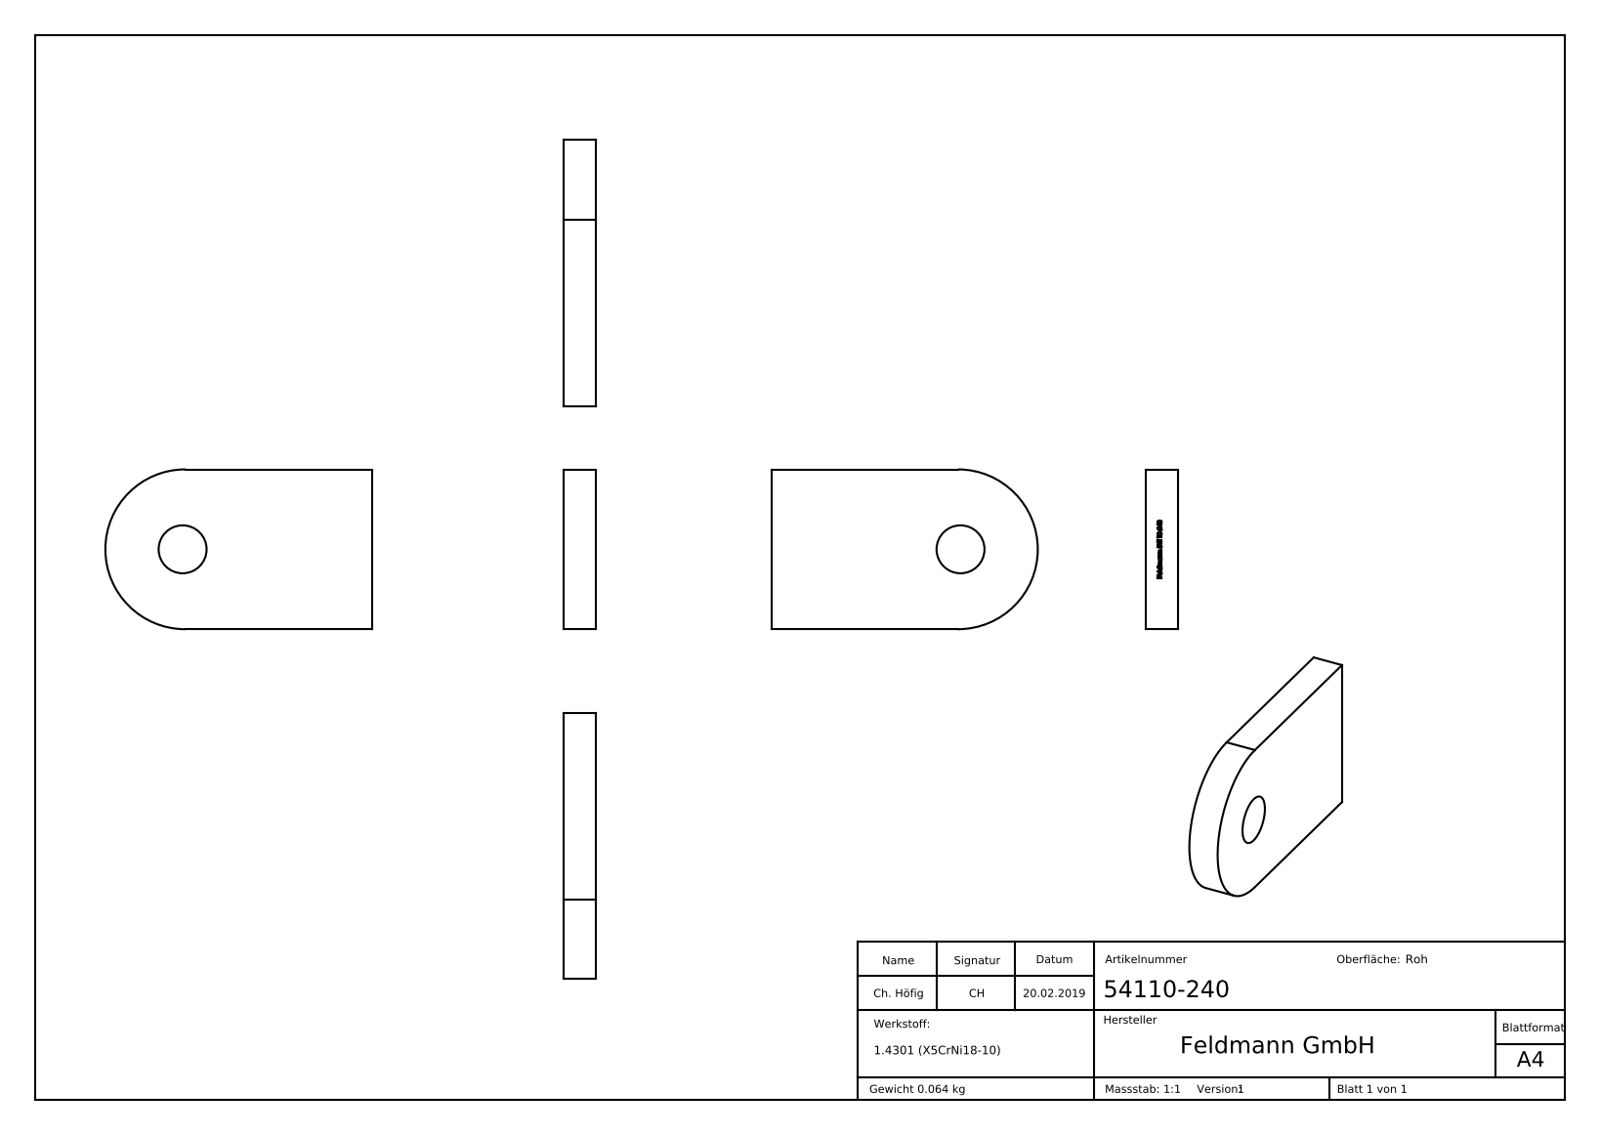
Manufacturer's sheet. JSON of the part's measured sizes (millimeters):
{"part_name": "54110-240", "step_written_by": "SolidWorks 2015 (CONFIG_CONTROL_DESIGN)", "units": "millimeters", "bodies": {"solids": 1, "faces": 221, "planar": 137, "cylindrical": 4, "other": 80}, "overall_size": [50, 30, 6], "volume_mm3": 8039, "surface_area_mm2": 3738, "round_holes": [[9, 1]], "partial_cylinders_radius": [[15, 1]], "face_to_face_distances": [6, 30, 3, 0.53, 0.61, 2.82, 2.61, 1.21, 0.83, 0.4]}
